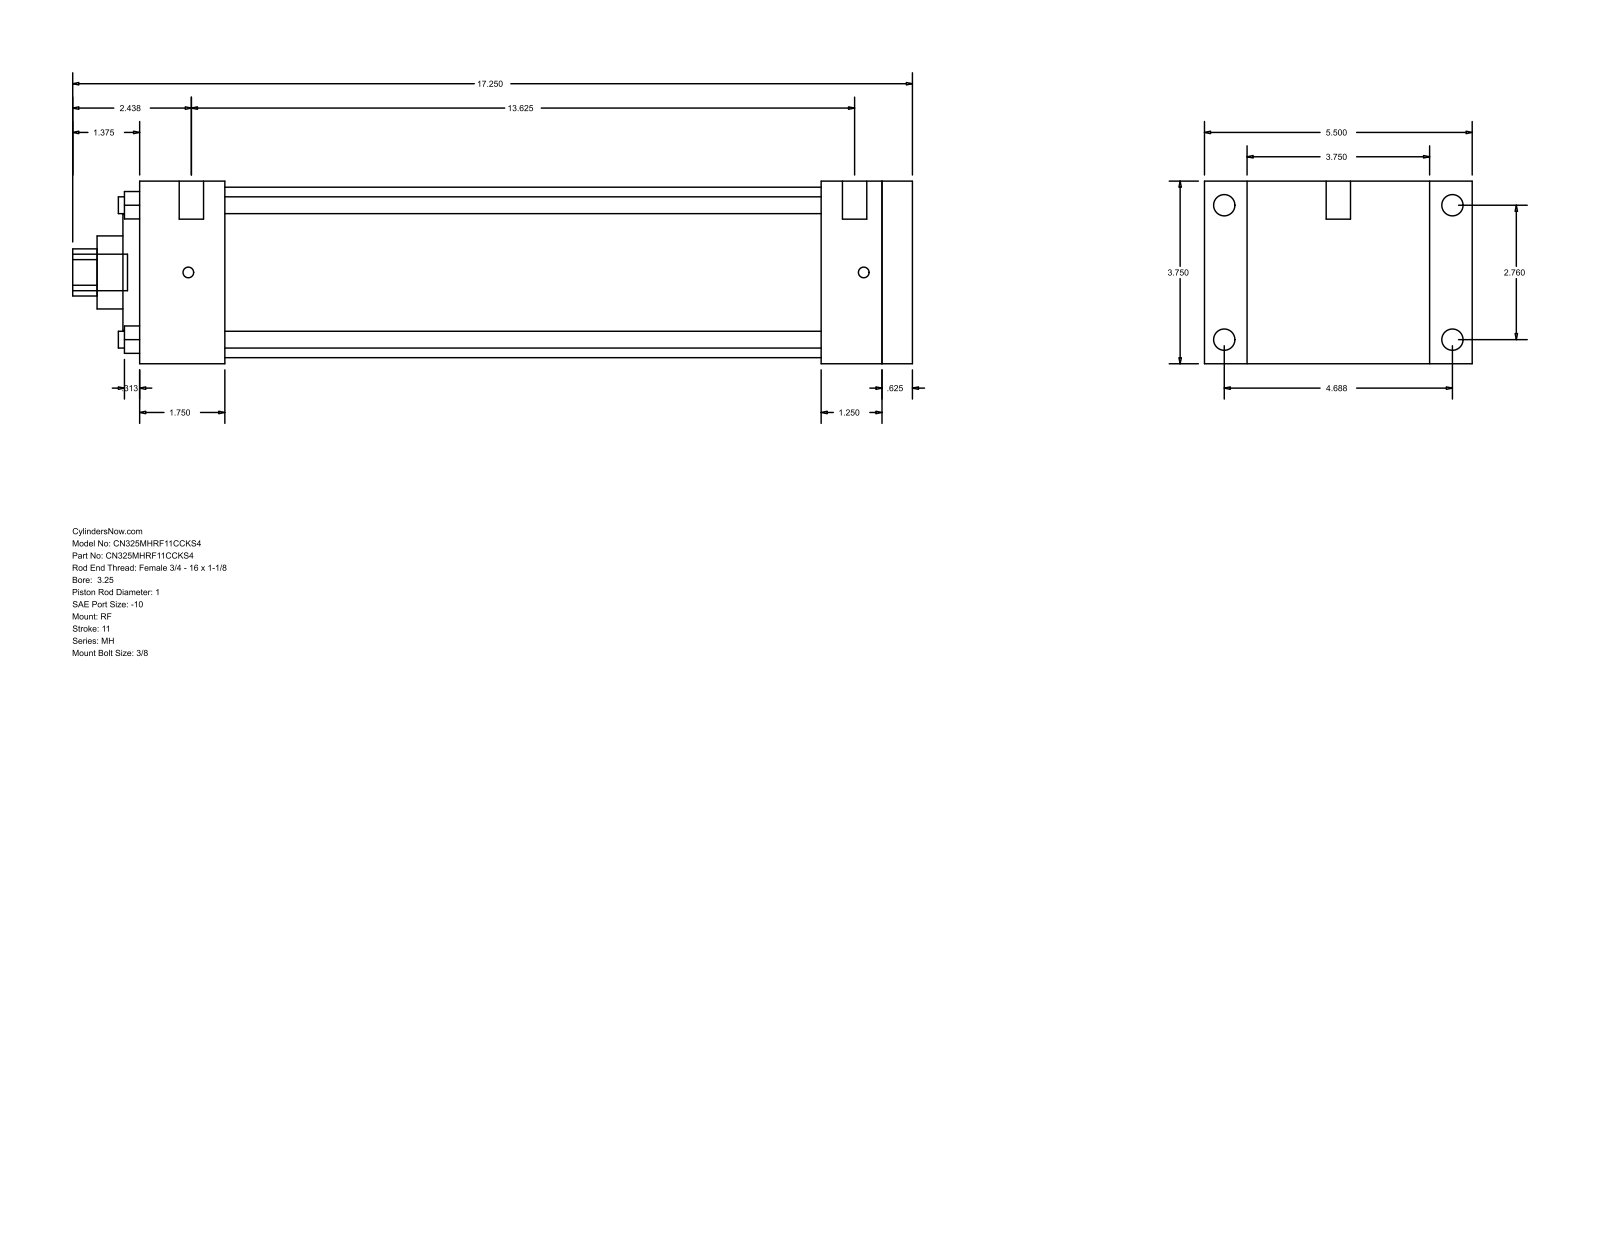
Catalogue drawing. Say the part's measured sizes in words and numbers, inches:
The part is named "MH_RF__0325_1". Its 3-D file was written by "GSSL Pune (CONFIG_CONTROL_DESIGN)". It is 0 solids with 94 faces: 65 planar, 29 cylindrical and 0 other. Overall it measures 17.25 by 5.5 by 3.75 inches. Round holes: 4 of diameter 0.345, 1 of diameter 1, 1 of diameter 1.5, 1 of diameter 2.375, 1 of diameter 3.5. Round bosses or shafts: 4 of diameter 0.438, 4 of diameter 0.219, 2 of diameter 0.5, 1 of diameter 0.75. Partial cylindrical surfaces (rounded edges, fillets, slot ends): 1 of radius 0.484. The main face-to-face distances are 3.75, 15.875, 15.25, 0.625, 0.875, 4.625, 1.75, 13.5, 14.125, 14. The hole center spacings are 1.952, 2.76, 3.903.
